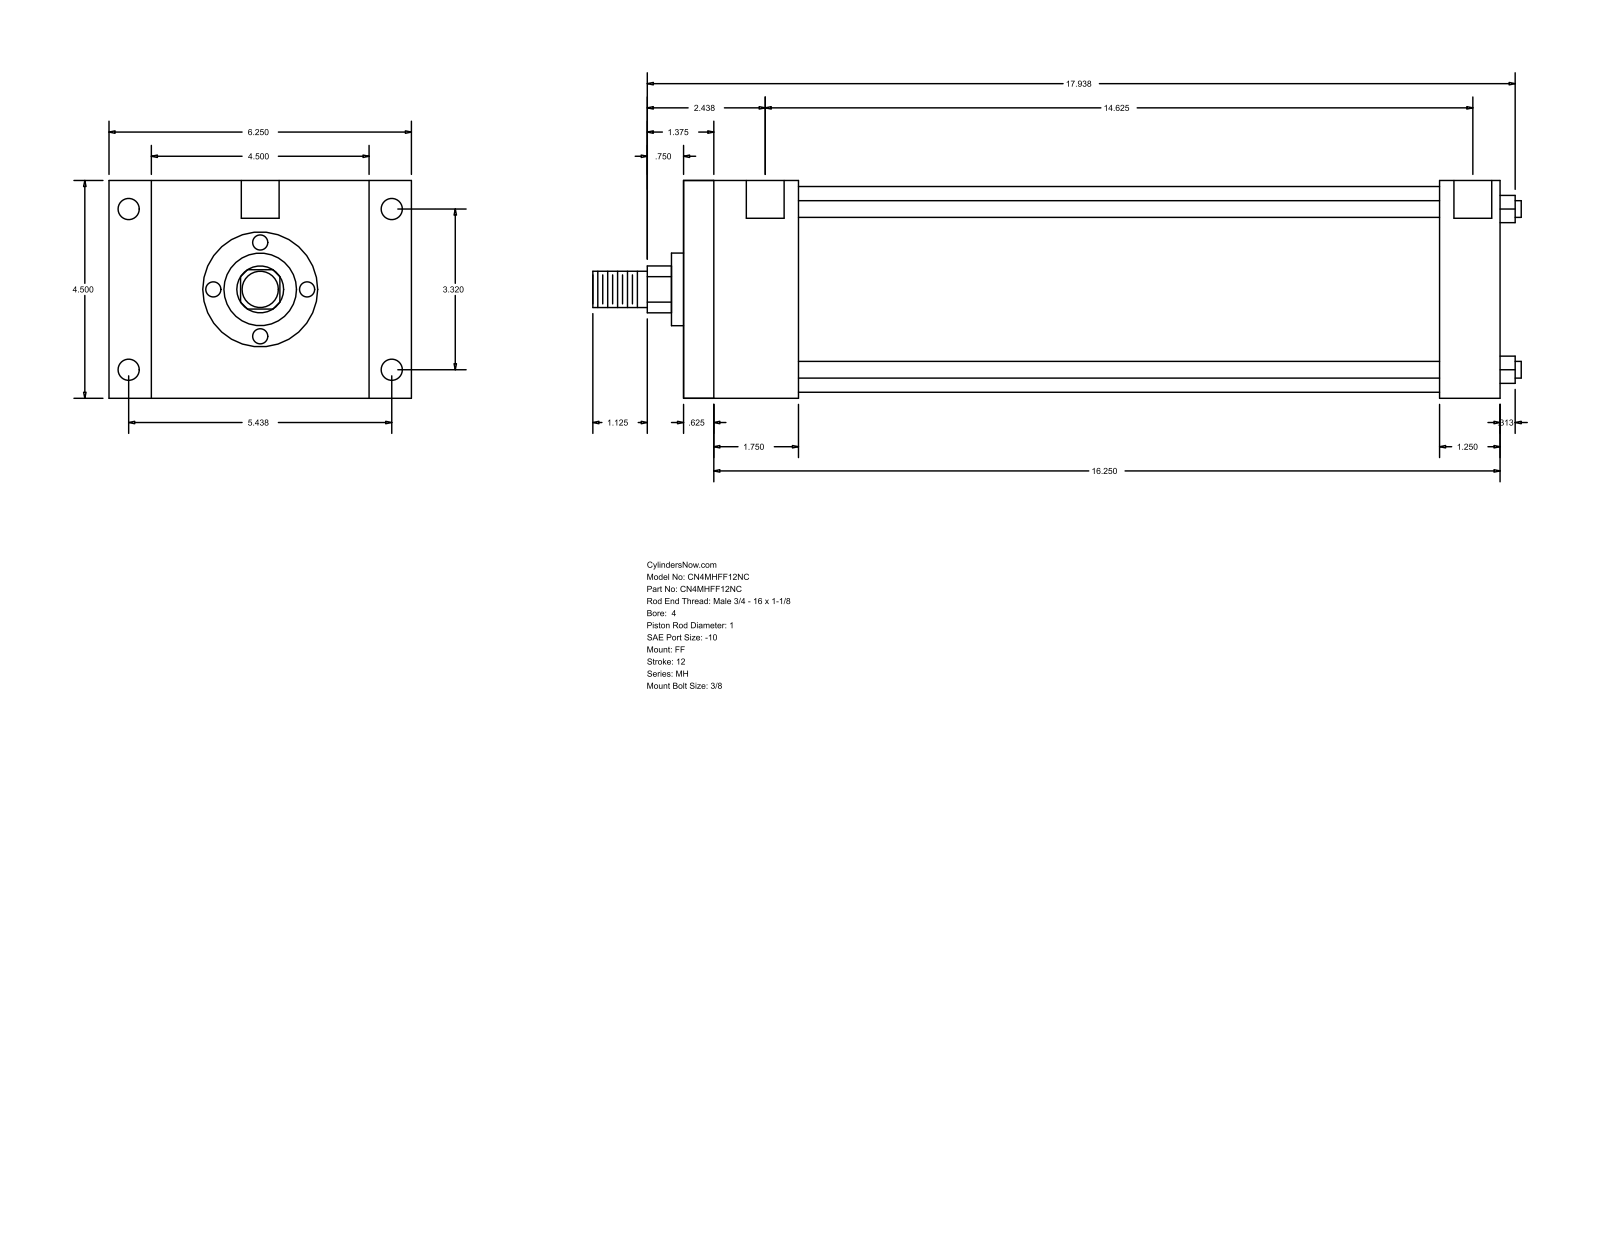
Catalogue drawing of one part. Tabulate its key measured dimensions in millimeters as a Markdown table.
| quantity | value |
| --- | --- |
| part name | MH_FF__0400_1 |
| STEP written by | GSSL Pune (CONFIG_CONTROL_DESIGN) |
| units | millimeters |
| bodies | 0 solids, 92 faces (64 planar, 28 cylindrical, 0 other) |
| overall size | 487.36 × 158.75 × 114.3 |
| round holes (diameter × count) | 8.73 × 4, 11.13 × 4, 19.84 × 2 |
| round bosses / shafts (diameter × count) | 8.76 × 4, 107.95 × 1, 38.1 × 1, 25.4 × 1, 19.05 × 1 |
| partial cylindrical surfaces (radius × count) | 12.29 × 1 |
| main face-to-face distances | 114.3, 428.63, 15.87, 412.76, 60.33, 44.46, 368.3, 396.88, 381.01, 336.55 |
| hole center spacings | 84.32, 138.12, 161.82, 374.65, 1.58, 1.59, 371.48, 373.06 |
